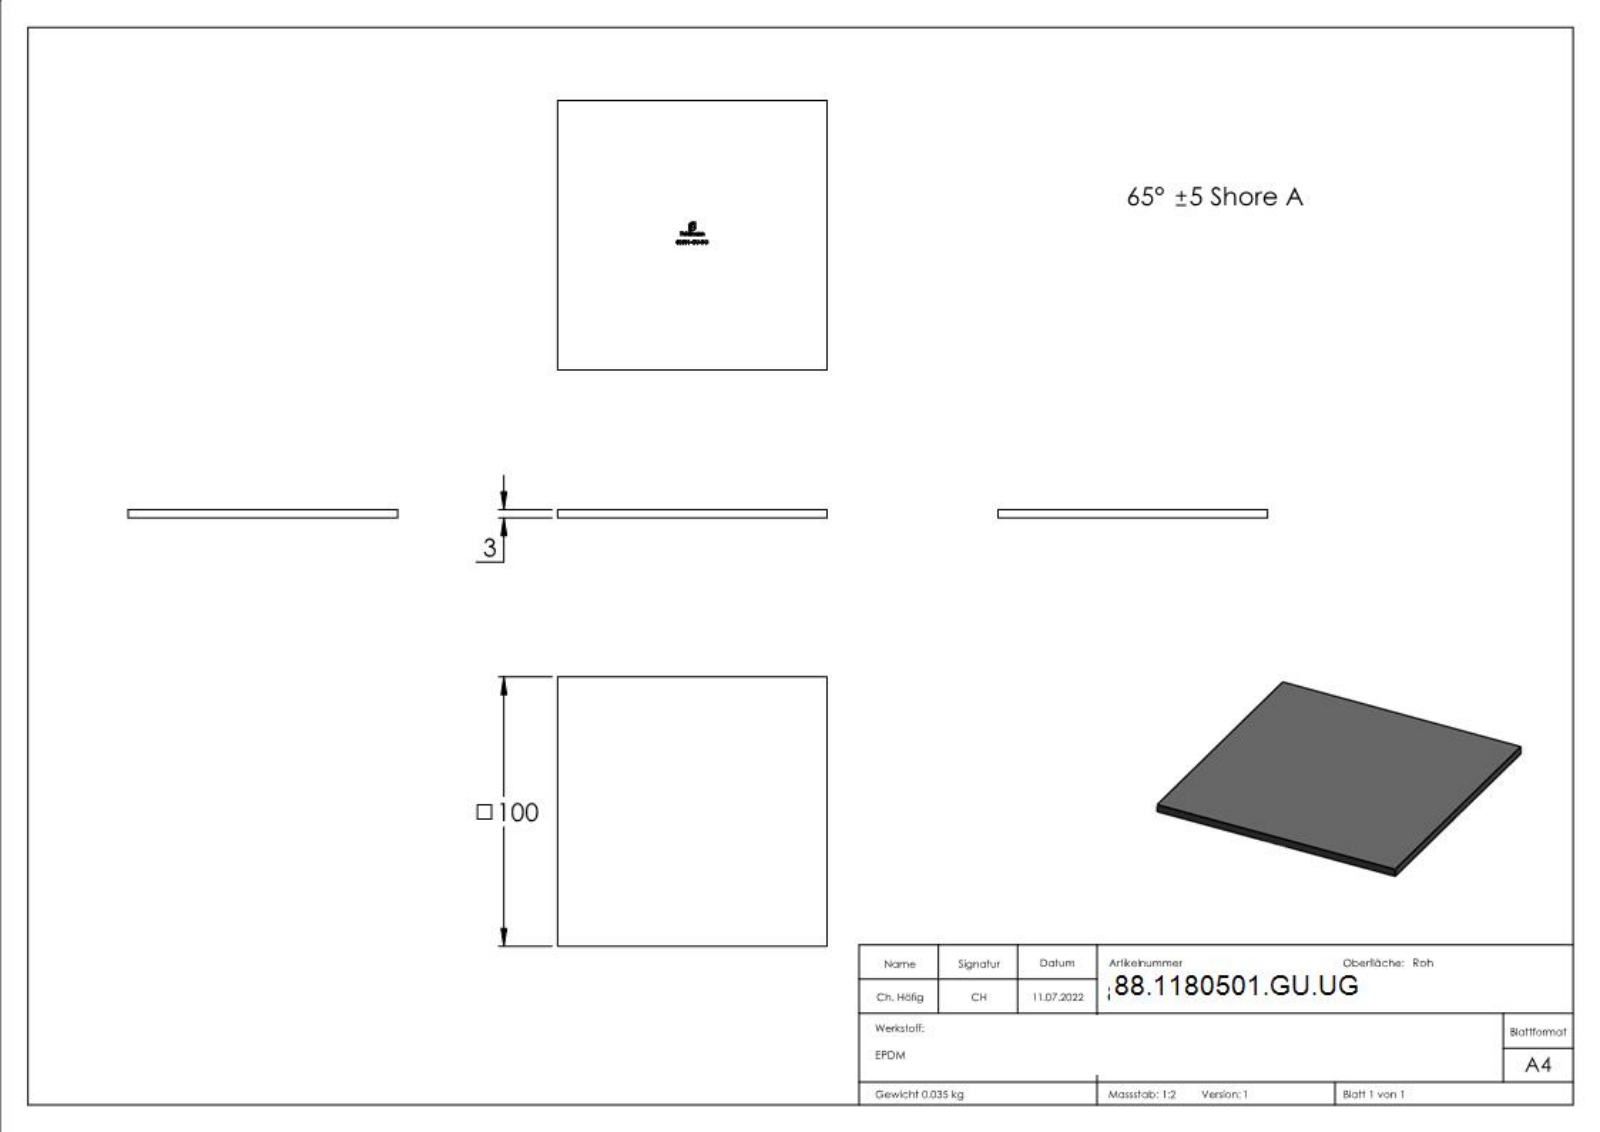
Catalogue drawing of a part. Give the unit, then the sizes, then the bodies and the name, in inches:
Units: inches
Overall size (bounding box): 3.937 × 3.937 × 0.118
Main face-to-face distances: 0.118, 3.937, 0.114, 0.029, 0.027, 0.106, 0.013, 0.126, 1.969, 1.929
Volume: 1.831 in³ · Surface area: 32.88 in²
Bodies: 1 solid, 292 faces (149 planar, 0 cylindrical, 143 other)
Part name (STEP PRODUCT): 80501-GU-UG
STEP written by: SolidWorks 2018 (CONFIG_CONTROL_DESIGN)
